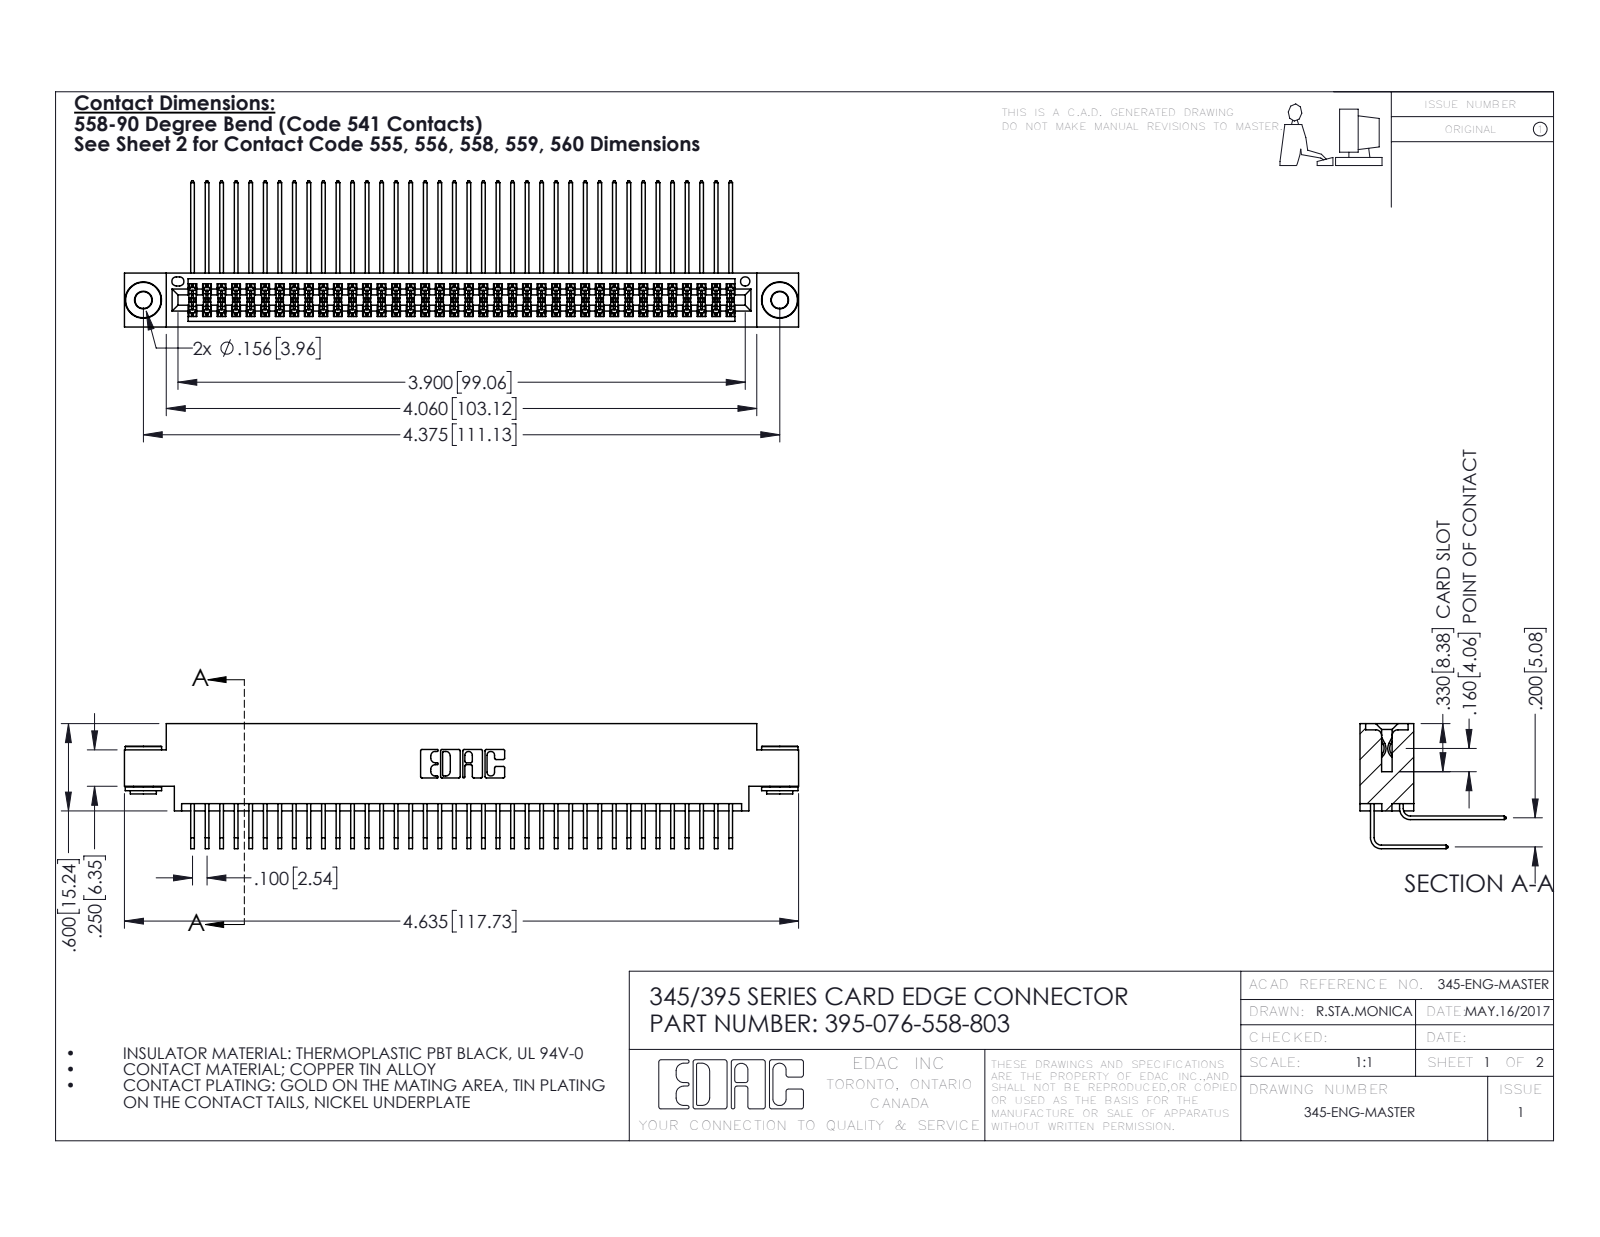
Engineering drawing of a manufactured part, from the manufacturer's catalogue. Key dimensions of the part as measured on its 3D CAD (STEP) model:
Part name (STEP PRODUCT): 345-292-001_558 559 Tail - 1; 345 Part_0.170 Offset - 0.156 Dia-TH; 345-292-001_558 Tail - 2; 345-250-002_345-250-002-102 (+1 more)
STEP written by: SolidWorks 2016 (CONFIG_CONTROL_DESIGN)
Units: inches
Bodies: 79 solids, 4120 faces (2754 planar, 1358 cylindrical, 8 other)
Overall size (bounding box): 4.635 × 1.005 × 0.859
Volume: 0.717 in³ · Surface area: 30.52 in²
Round holes (diameter × count): ⌀0.116 ×2, ⌀0.156 ×2, ⌀0.064 ×1
Round bosses / shafts (diameter × count): ⌀0.25 ×2, ⌀0.18 ×2, ⌀0.136 ×2
Partial cylindrical surfaces — rounded edges, fillets, slot ends (radius × count): R0.006 ×114, R0.01 ×22, R0.007 ×6, R0.031 ×6, R0.026 ×3, R0.014 ×2, R0.019 ×2, R0.022 ×2
Main face-to-face distances: 0.072, 0.298, 0.2, 0.37, 0.098, 0.272, 0.025, 0.225, 0.175, 0.025
Hole centre spacings: 0.27, 4.139, 4.375
